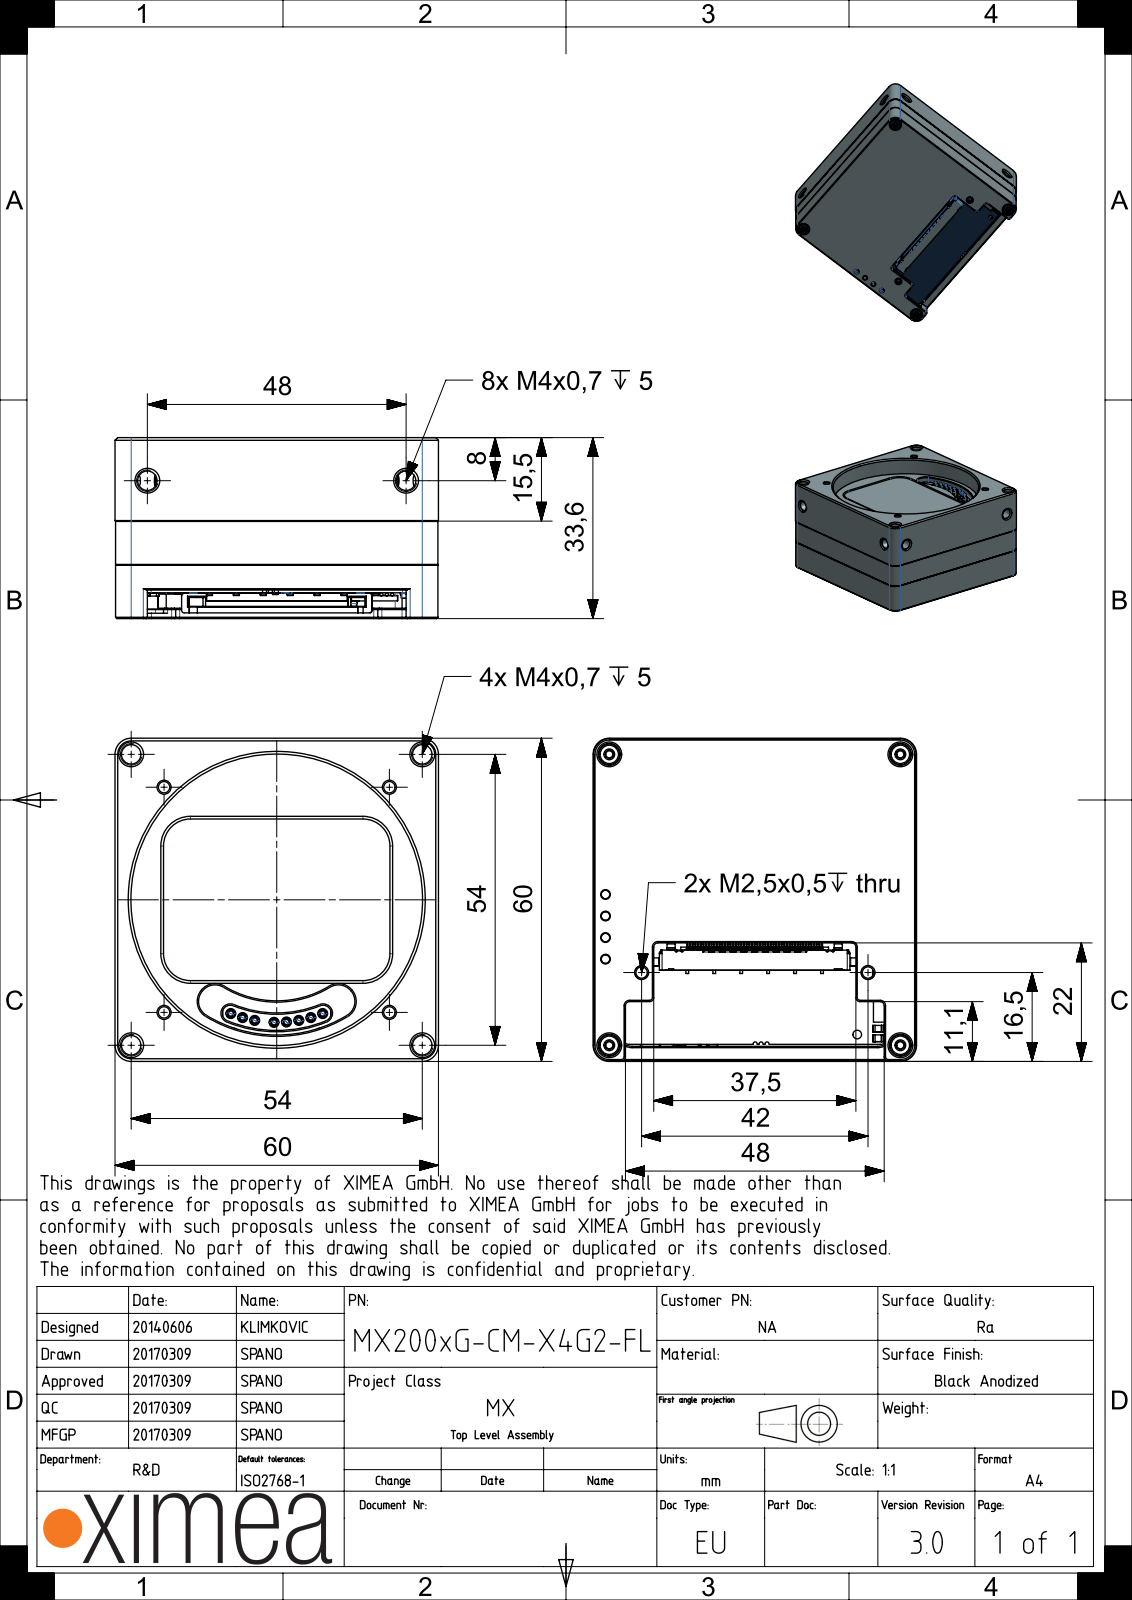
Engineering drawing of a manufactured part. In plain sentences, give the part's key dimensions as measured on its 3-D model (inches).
The part is named "MECH-GASKET-CB200; SROB-M2X20-IMBUS-STNLS; MECH-MX200-REAR; PCA-MX-X4G2-Main-LIGHTWEIGHT (+8 more)". Its 3-D file was written by "SIEMENS PLM Software NX 11.0 (AUTOMOTIVE_DESIGN)". It is 42 solids with 4181 faces: 2500 planar, 1052 cylindrical and 629 other. Overall it measures 2.362 by 2.362 by 1.323 inches. Its volume is 3.191 cubic inches and its surface area 99.79 square inches. Round holes: 20 of diameter 0.063, 10 of diameter 0.083, 9 of diameter 0.051, 8 of diameter 0.036, 8 of diameter 0.043, 8 of diameter 0.051, 8 of diameter 0.142, 6 of diameter 0.079, 4 of diameter 0.028, 4 of diameter 0.035, 4 of diameter 0.043, 4 of diameter 0.091. Round bosses or shafts: 143 of diameter 0.018, 8 of diameter 0.072, 8 of diameter 0.061, 8 of diameter 0.059, 8 of diameter 0.049, 8 of diameter 0.042, 4 of diameter 0.217, 4 of diameter 0.15. Partial cylindrical surfaces (rounded edges, fillets, slot ends): 70 of radius 0.059, 59 of radius 0.02, 35 of radius 0.118, 30 of radius 0.008, 20 of radius 0.004, 14 of radius 0.03, 12 of radius 0.197, 9 of radius 0.016. The main face-to-face distances are 0.039, 0.284, 0.352, 0.374, 0.324, 2.358, 0.035, 2.323, 0.244, 0.245. The hole center spacings are 1.901, 0.091, 0.34, 0.896, 0.896, 1.164, 1.503, 1.646.
